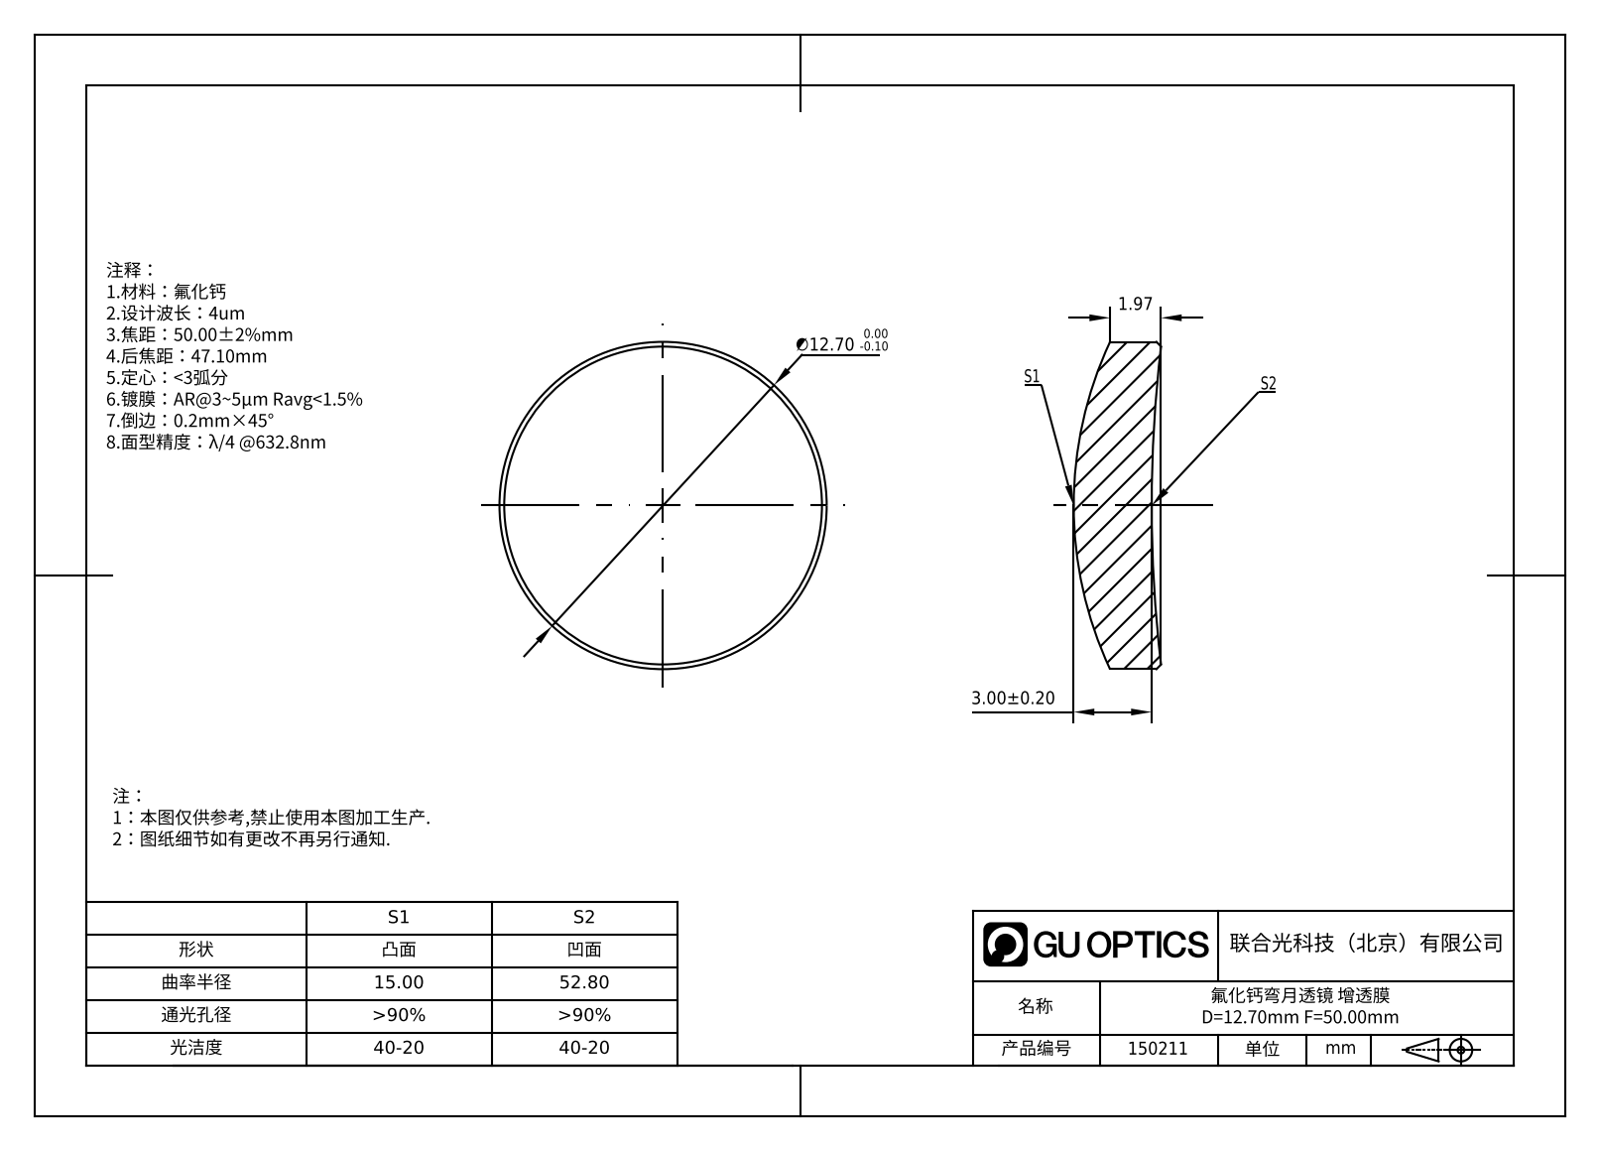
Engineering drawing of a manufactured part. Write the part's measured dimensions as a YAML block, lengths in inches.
part_name: "GLM5-012B-050-IR1"
step_written_by: "SolidWorks 2022 (AUTOMOTIVE_DESIGN)"
units: inches
bodies: {solids: 1, faces: 8, planar: 0, cylindrical: 2, other: 6}
overall_size: [0.5, 0.5, 0.133]
volume: 0.019
surface_area: 0.519
round_bosses_or_shafts:
  - {diameter: 0.5, count: 1}
